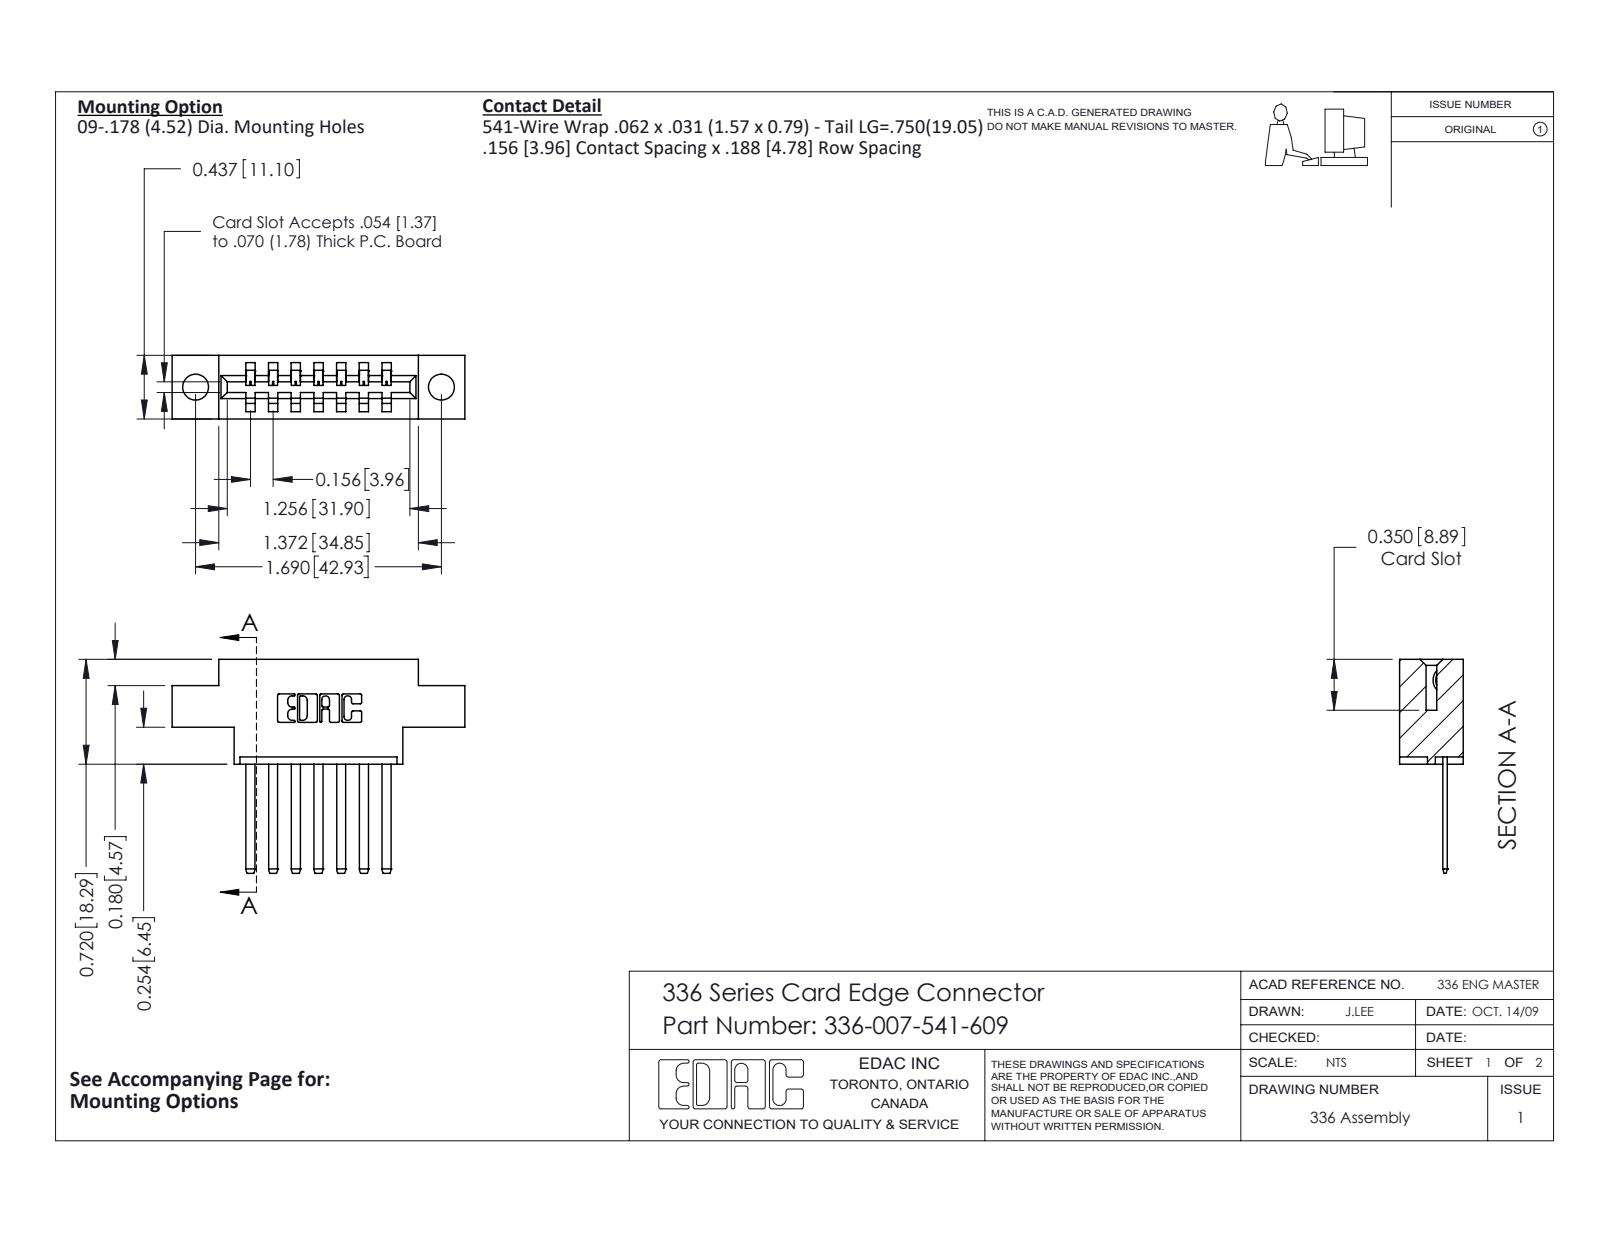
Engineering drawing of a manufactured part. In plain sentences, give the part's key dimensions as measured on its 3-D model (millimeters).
The part is named "336-007-541-609; 336 Part_Offset - .178 Dia - TH; 336-290-001_336-290-541". Its 3-D file was written by "SolidWorks 2020 (CONFIG_CONTROL_DESIGN)". It is 8 solids with 468 faces: 312 planar, 156 cylindrical and 0 other. Overall it measures 51.1 by 37.3 by 11.1 millimeters. Its volume is 6 290 cubic millimeters and its surface area 6 355 square millimeters. Round holes: 2 of diameter 4.5. Partial cylindrical surfaces (rounded edges, fillets, slot ends): 22 of radius 0.3, 14 of radius 0.1, 14 of radius 1.4, 6 of radius 0.2, 6 of radius 0.8, 3 of radius 0.7, 2 of radius 0.6, 2 of radius 1. The main face-to-face distances are 4, 11.1, 7.9, 5.6, 7.9, 11.9, 15.8, 4.6, 6.5, 1.6. The hole center spacings are 42.9.
